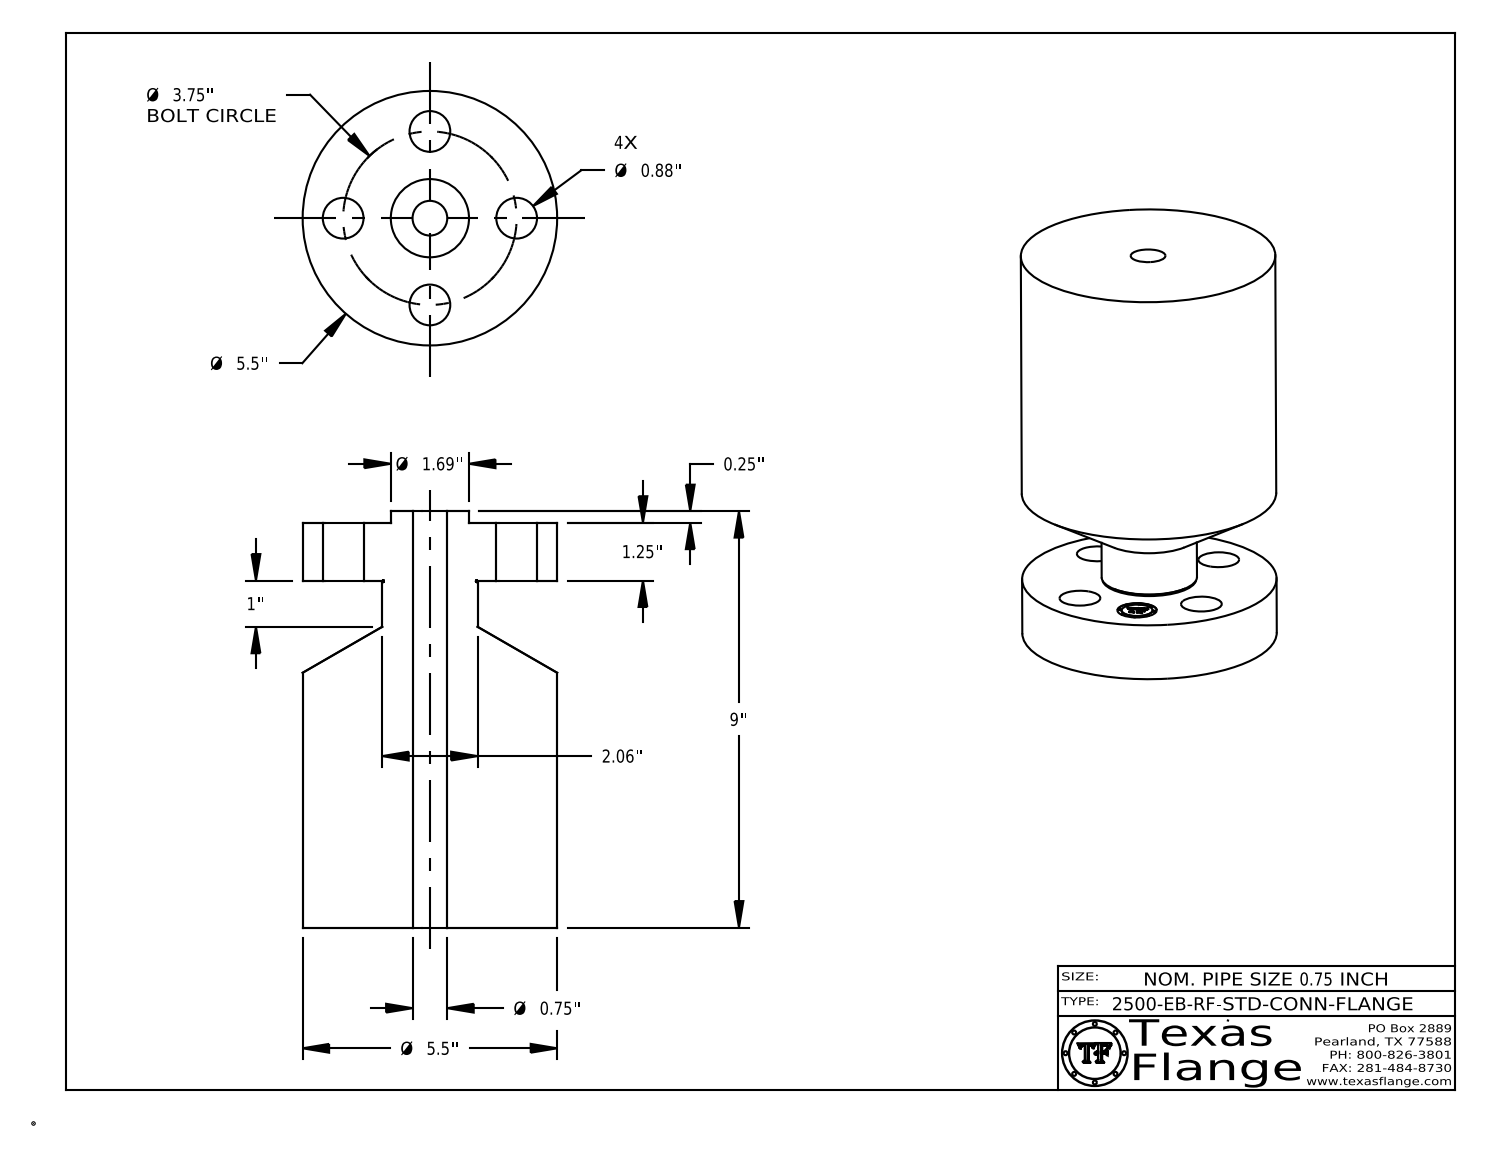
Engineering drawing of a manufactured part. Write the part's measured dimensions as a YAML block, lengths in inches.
part_name: "0.75-2500-EB-RF-STD-CONN-FLANGE"
step_written_by: "CATIA V5 STEP AP214 (AUTOMOTIVE_DESIGN)"
units: inches
bodies: {solids: 1, faces: 413, planar: 369, cylindrical: 38, other: 6}
overall_size: [9, 5.5, 5.5]
volume: 169.3
surface_area: 245.7
round_holes:
  - {diameter: 0.88, count: 4}
  - {diameter: 0.75, count: 1}
  - {diameter: 0.85, count: 1}
round_bosses_or_shafts:
  - {diameter: 0.051, count: 8}
  - {diameter: 5.5, count: 1}
  - {diameter: 2.06, count: 1}
  - {diameter: 1.69, count: 1}
  - {diameter: 0.67, count: 1}
face_to_face_distances: [8.75, 1.25, 7.5, 0.25, 1.5, 9, 1.495, 1.245, 7.505, 0.254]
hole_center_spacings: [1.875, 2.652, 1.435, 3.465, 3.75]
